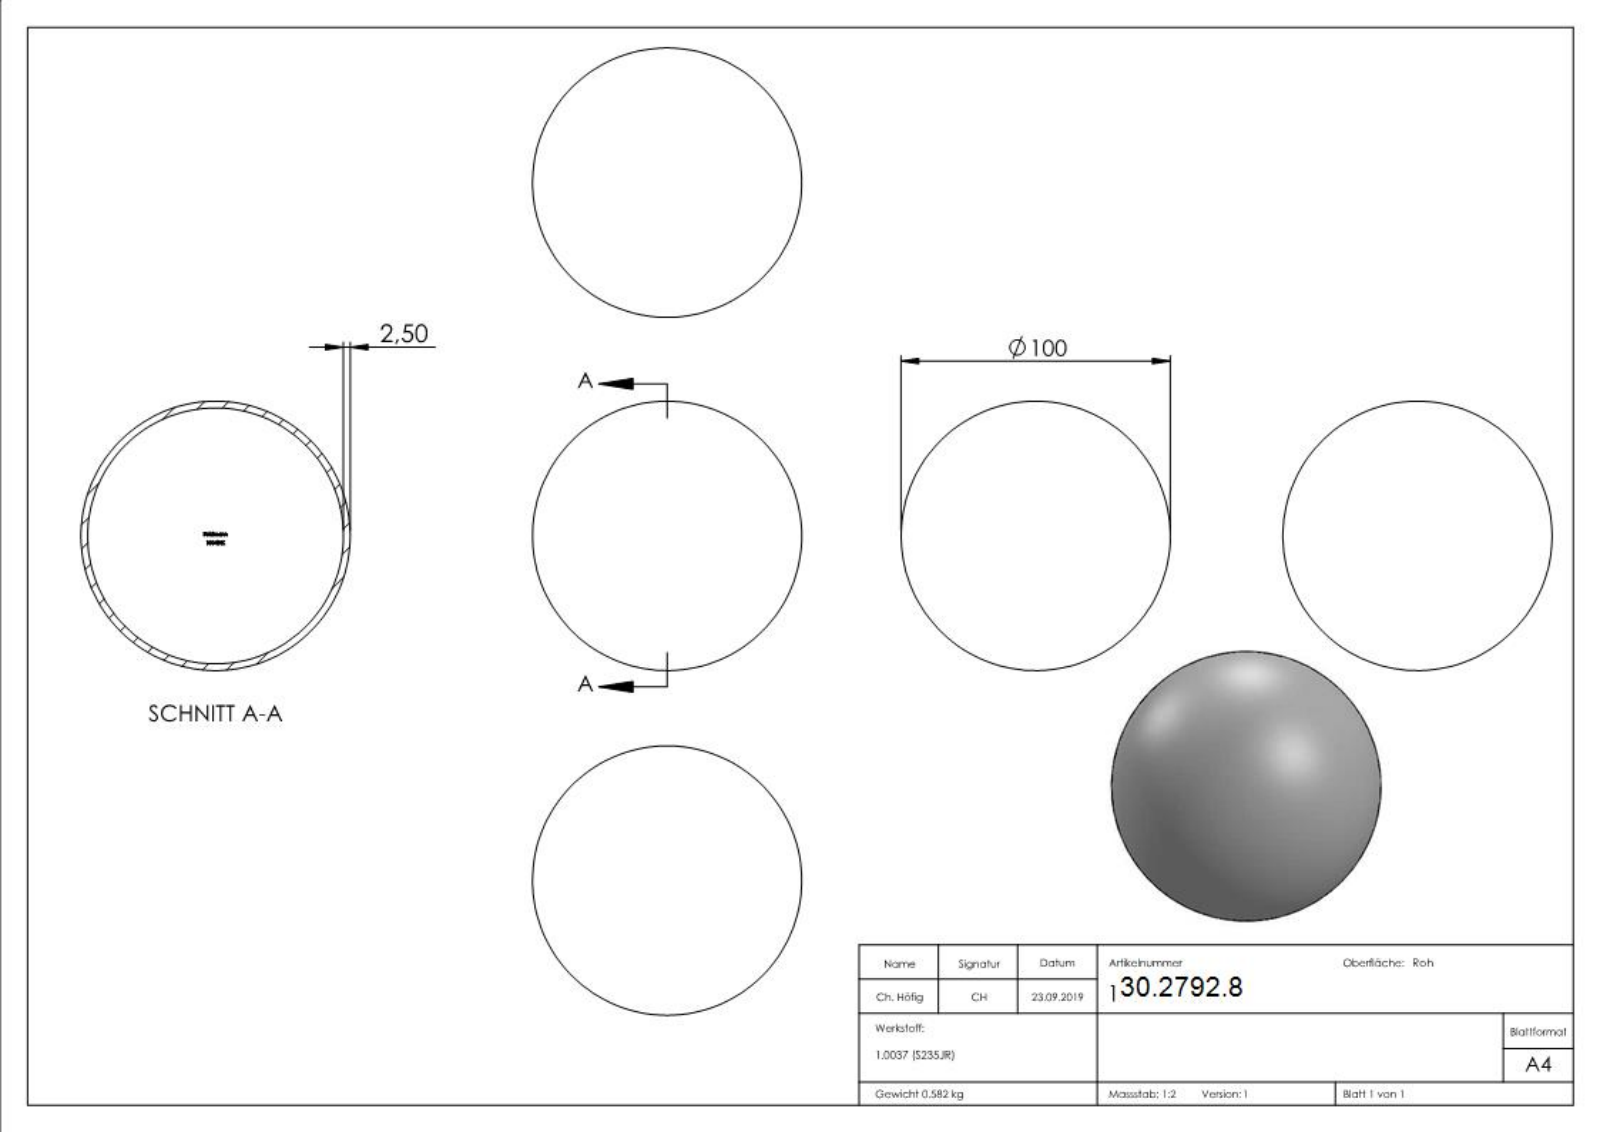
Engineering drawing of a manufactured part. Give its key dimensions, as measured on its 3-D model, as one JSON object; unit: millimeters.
{"part_name": "100-EHK", "step_written_by": "SolidWorks 2015 (CONFIG_CONTROL_DESIGN)", "units": "millimeters", "bodies": {"solids": 1, "faces": 191, "planar": 99, "cylindrical": 0, "other": 92}, "overall_size": [100, 100, 100], "volume_mm3": 74678, "surface_area_mm2": 59777, "face_to_face_distances": [3.2, 1.26, 4.36, 4.5, 5.62, 0.78, 0.46, 3.59, 2.03, 3.13]}
